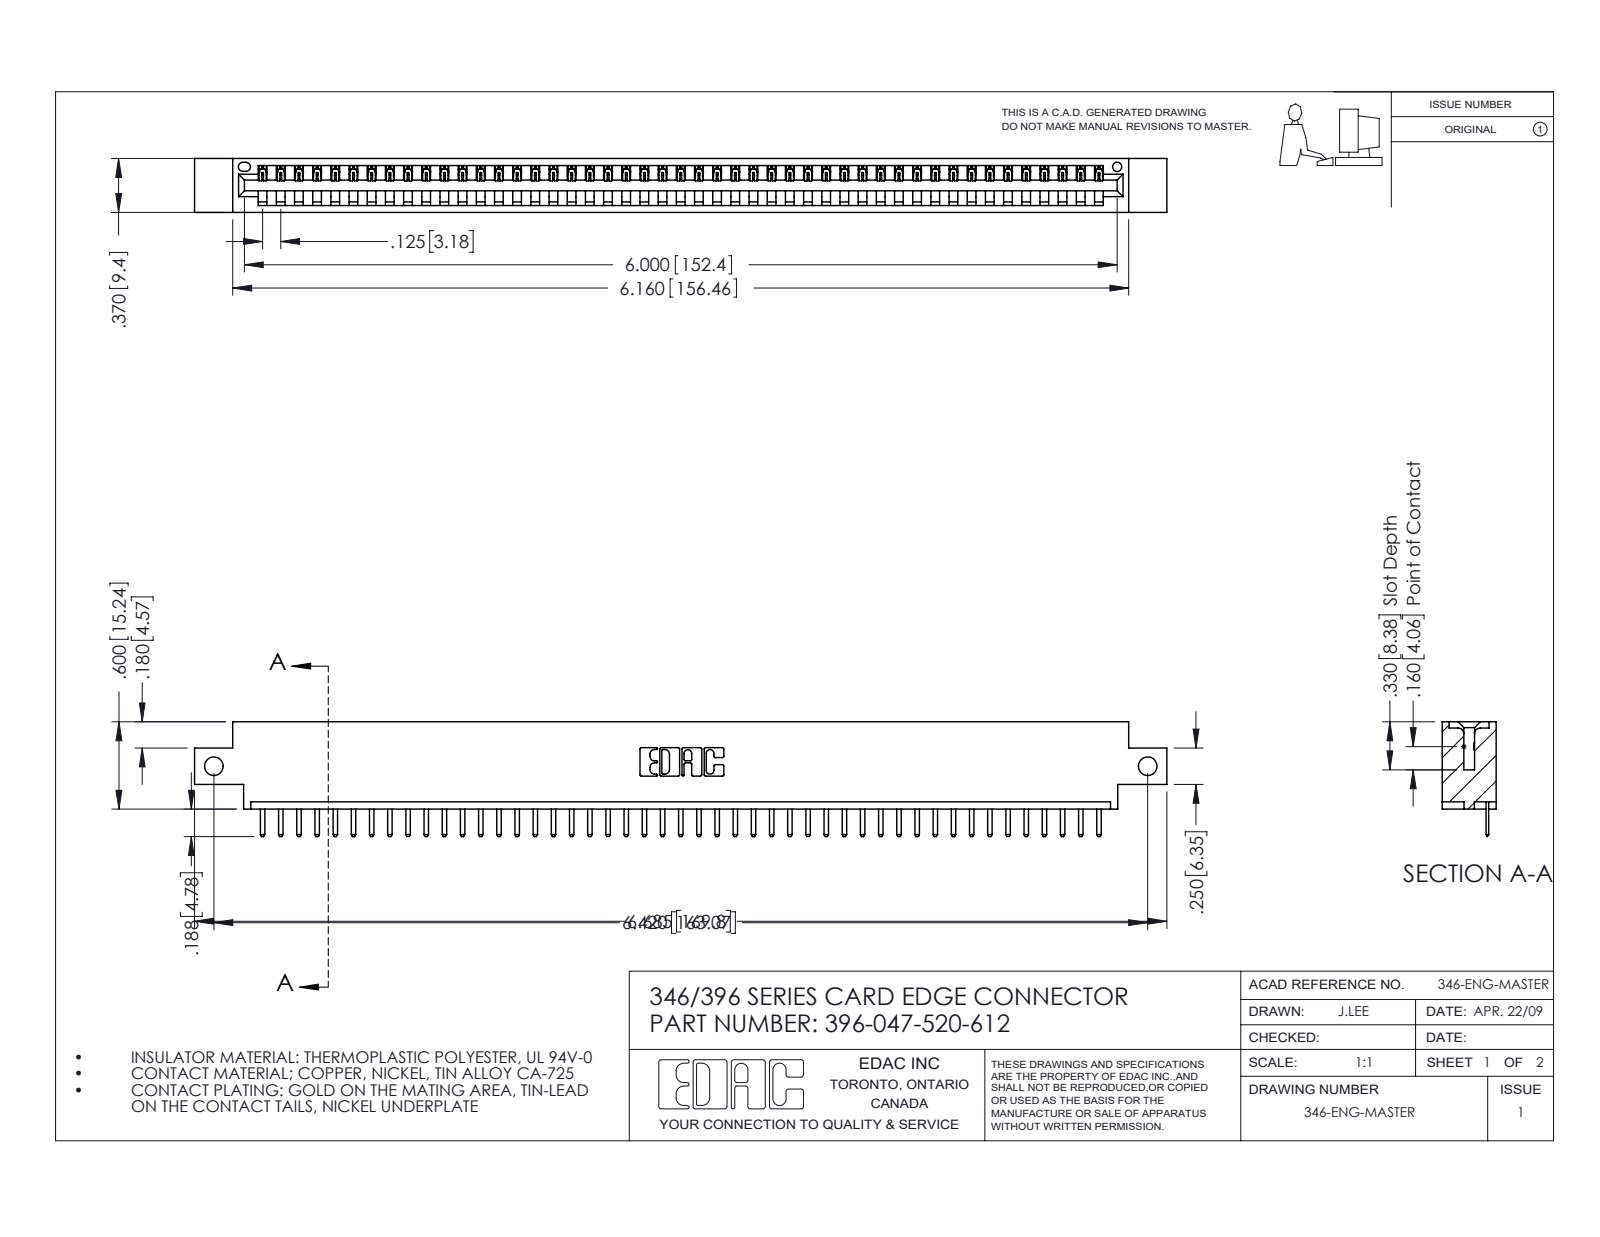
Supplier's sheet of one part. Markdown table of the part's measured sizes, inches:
| quantity | value |
| --- | --- |
| part name | 345-292-001_345-293-120; 346 Part_0.170 Offset - Side Mount; 396-047-520-612 |
| STEP written by | SolidWorks 2016 (CONFIG_CONTROL_DESIGN) |
| units | inches |
| bodies | 48 solids, 3040 faces (2054 planar, 986 cylindrical, 0 other) |
| overall size | 6.685 × 0.788 × 0.37 |
| volume | 0.971 in³ |
| surface area | 30.23 in² |
| round holes (diameter × count) | 0.128 × 2, 0.064 × 1 |
| partial cylindrical surfaces (radius × count) | 0.01 × 96, 0.006 × 94, 0.01 × 22, 0.007 × 6, 0.031 × 6, 0.026 × 3, 0.031 × 2, 0.04 × 2 |
| main face-to-face distances | 0.048, 0.322, 0.37, 0.25, 0.148, 0.222, 0.1, 0.174, 0.072, 0.298 |
| hole center spacings | 6.42 |
